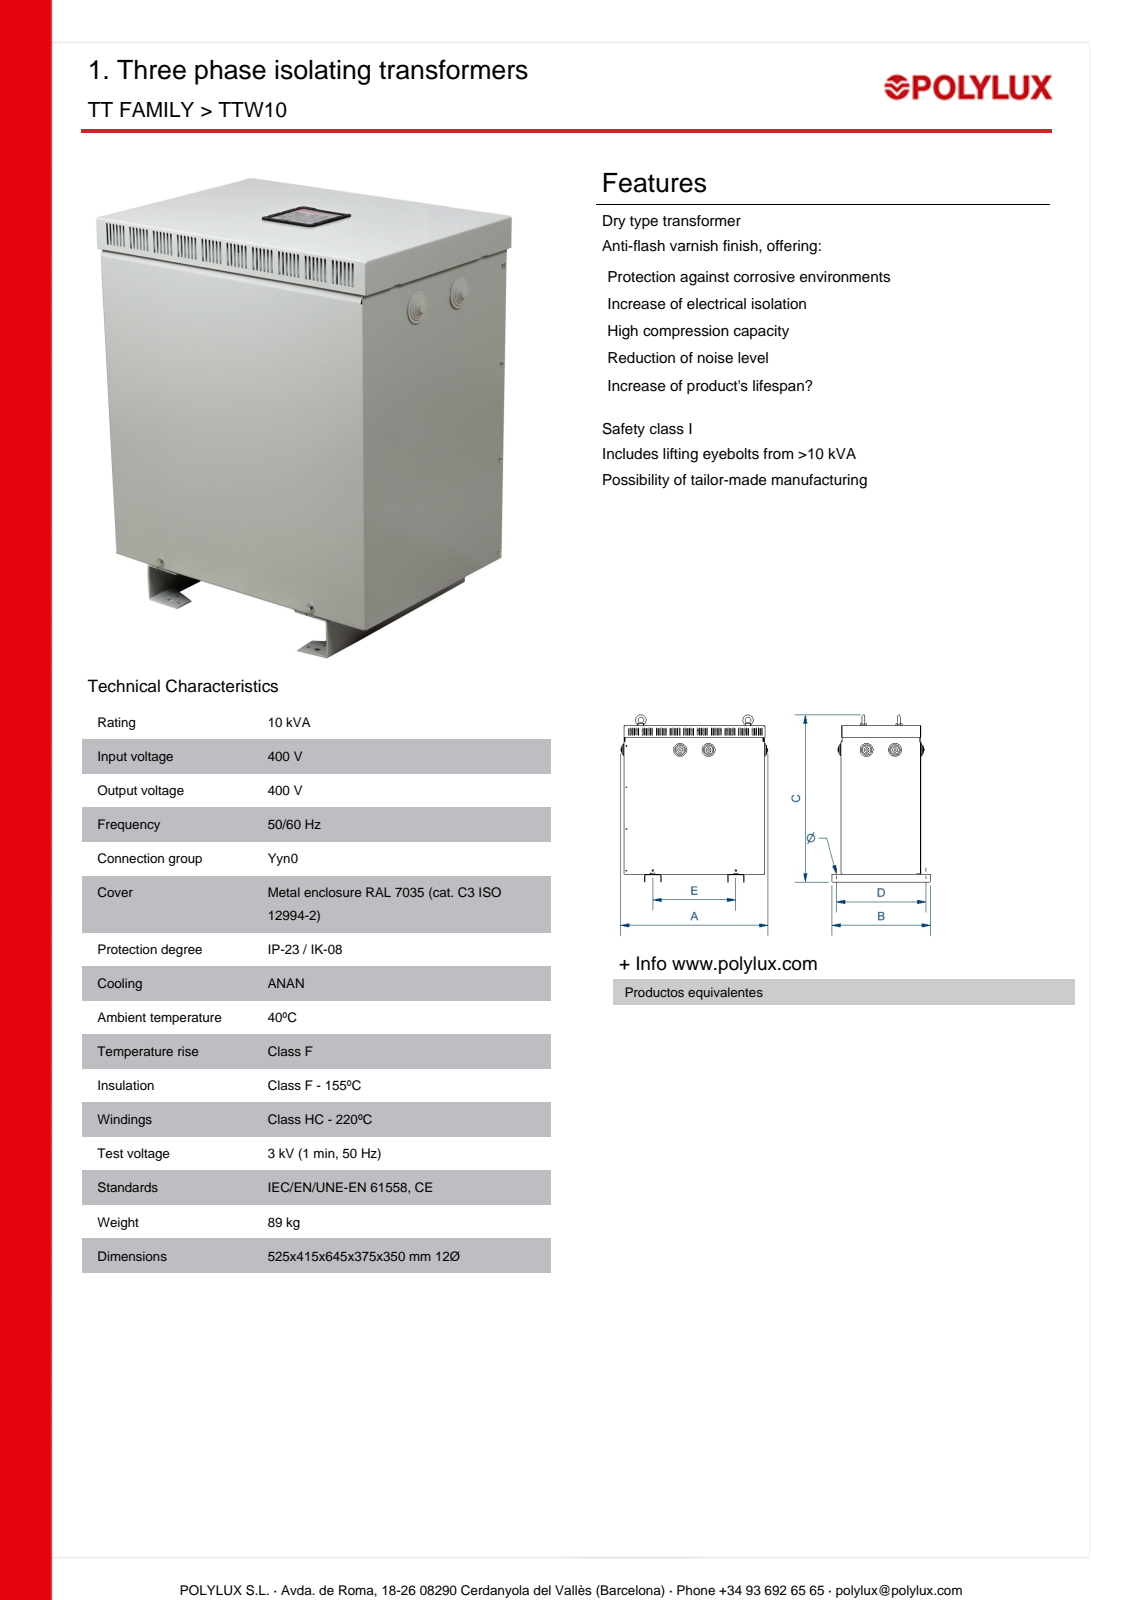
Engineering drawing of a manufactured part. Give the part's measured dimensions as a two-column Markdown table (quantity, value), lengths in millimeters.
| quantity | value |
| --- | --- |
| part name | CAJ23RC70-1E-V04+ Tornilleria |
| STEP written by | Autodesk Inventor 2018 (AUTOMOTIVE_DESIGN) |
| units | millimeters |
| bodies | 51 solids, 1531 faces (888 planar, 477 cylindrical, 166 other) |
| overall size | 641.5 × 548.5 × 426.7 |
| volume | 2 627 000 mm³ |
| surface area | 3 289 000 mm² |
| round holes (diameter × count) | 5.5 × 12, 9 × 10, 6.8 × 8, 6.4 × 6, 6 × 4, 6.5 × 4, 7.5 × 4, 12 × 4, 20 × 4, 34 × 4, 43 × 4, 46.5 × 4 |
| round bosses / shafts (diameter × count) | 12 × 12, 6 × 8, 5 × 5, 56 × 4, 48.5 × 4, 45 × 4, 36 × 4, 22 × 4 |
| partial cylindrical surfaces (radius × count) | 1.5 × 125, 3 × 29, 2.5 × 8, 4.5 × 4, 6 × 4, 1 × 2, 4 × 2 |
| main face-to-face distances | 1.5, 413.5, 517, 3, 412, 415, 515.5, 518.5, 410.5, 416.5 |
| hole center spacings | 15, 20, 351.32, 30, 352.28, 0.5, 351, 28.28 |
